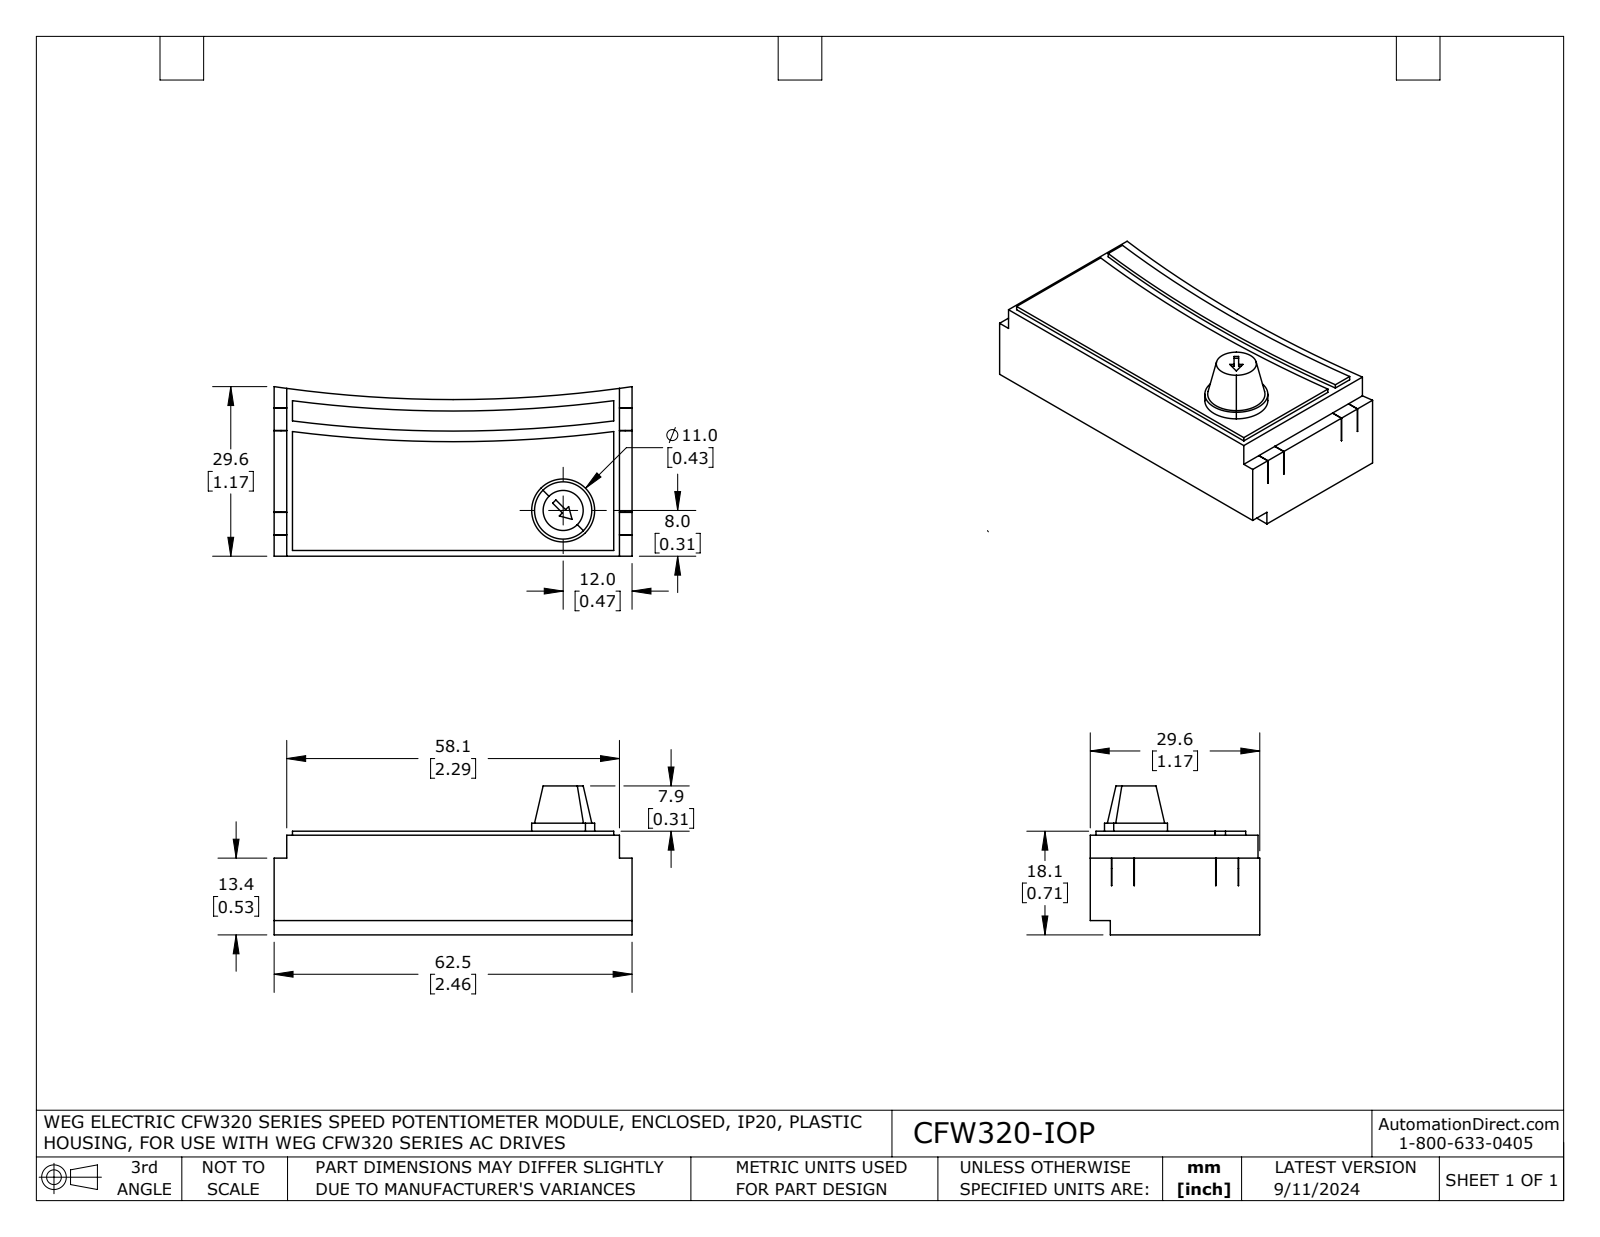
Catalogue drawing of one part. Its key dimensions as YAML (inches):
part_name: "CFW320 IOP"
step_written_by: "SolidWorks 2021 (AUTOMOTIVE_DESIGN)"
units: inches
bodies: {solids: 1, faces: 91, planar: 80, cylindrical: 8, other: 3}
overall_size: [2.461, 1.165, 1.024]
volume: 1.885
surface_area: 11.16
round_bosses_or_shafts:
  - {diameter: 0.433, count: 1}
partial_cylinders:
  - {radius: 8.543, count: 1}
  - {radius: 8.622, count: 1}
  - {radius: 8.76, count: 1}
  - {radius: 8.78, count: 1}
face_to_face_distances: [0.713, 2.461, 0.685, 0.028, 0.098, 0.087, 2.374, 0.587, 0.614, 0.157]
